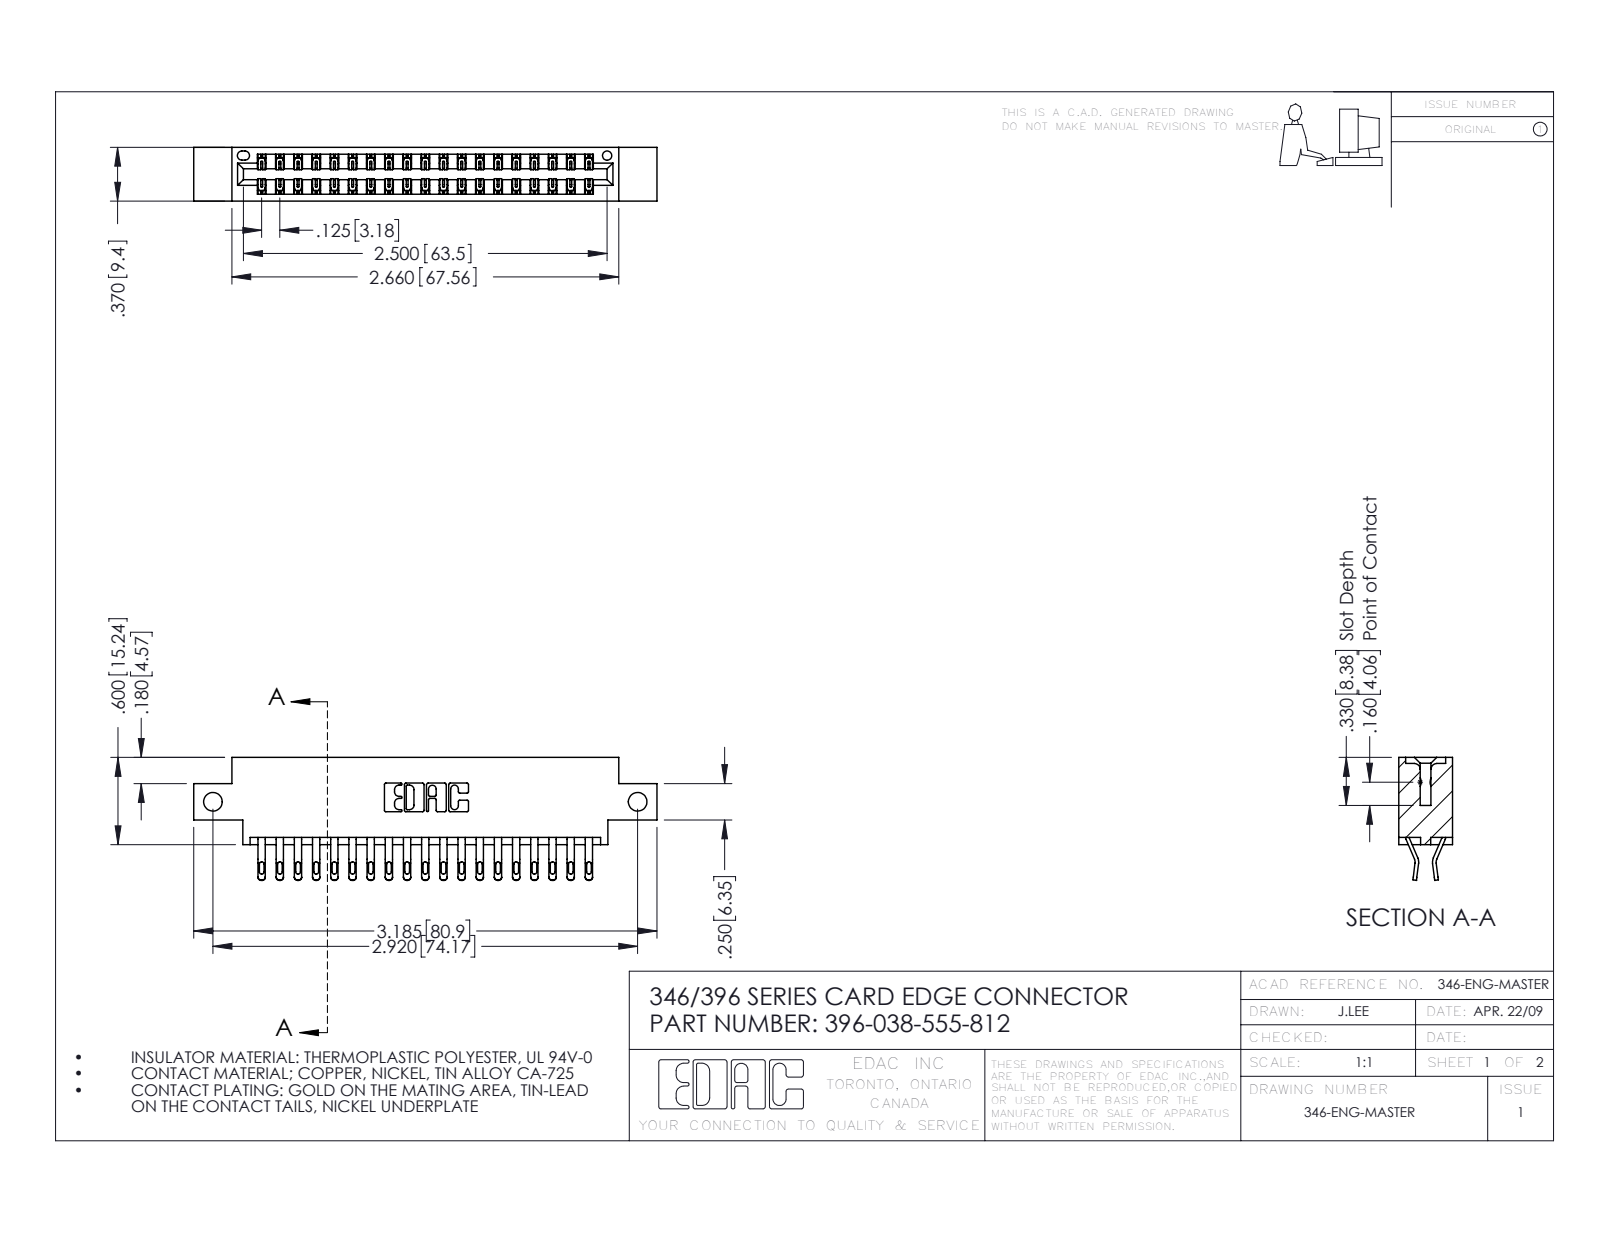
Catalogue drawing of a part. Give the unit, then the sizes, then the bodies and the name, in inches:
Units: inches
Overall size (bounding box): 3.185 × 0.845 × 0.37
Round holes (diameter × count): ⌀0.128 ×2, ⌀0.064 ×1
Partial cylindrical surfaces — rounded edges, fillets, slot ends (radius × count): R0.016 ×76, R0.02 ×76, R0.006 ×57, R0.01 ×22, R0.007 ×6, R0.031 ×6, R0.026 ×3, R0.01 ×2
Main face-to-face distances: 0.048, 0.322, 0.37, 0.25, 0.025, 0.072, 0.298, 0.275, 0.148, 0.222
Hole centre spacings: 2.92
Volume: 0.462 in³ · Surface area: 16.26 in²
Bodies: 39 solids, 2330 faces (1334 planar, 996 cylindrical, 0 other)
Part name (STEP PRODUCT): 346 Part_0.170 Offset - Side Mount; 396-038-555-812; 345-292-001_555 Tail
STEP written by: SolidWorks 2016 (CONFIG_CONTROL_DESIGN)
